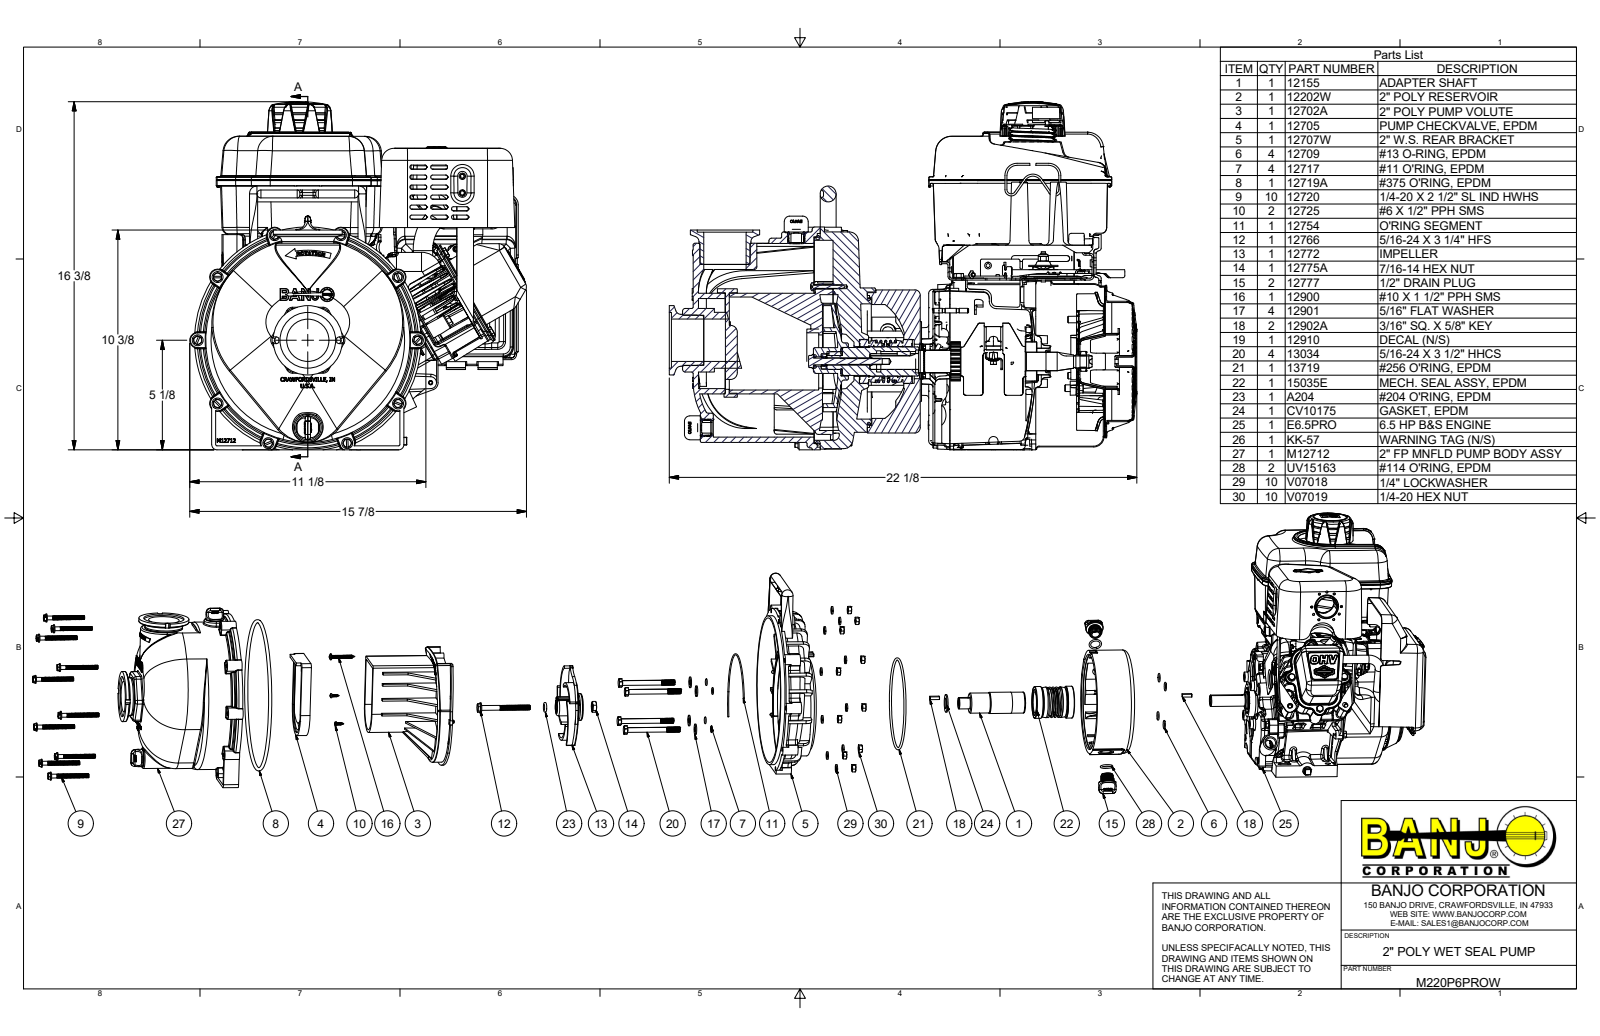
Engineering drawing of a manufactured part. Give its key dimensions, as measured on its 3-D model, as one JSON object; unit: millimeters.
{"part_name": "M220P6PROW; 12707W; 12707WX; 12703AWV (+8 more)", "step_written_by": "Autodesk Inventor 2017 (AUTOMOTIVE_DESIGN)", "units": "millimeters", "bodies": {"solids": 99, "faces": 21263, "planar": 5779, "cylindrical": 5805, "other": 9679}, "overall_size": [584.88, 417.62, 403.86], "volume_mm3": 3767000, "surface_area_mm2": 3383000, "round_holes": [[6.35, 13], [6.86, 11], [4.98, 10], [6.4, 10], [3.5, 9], [11.91, 8], [3.56, 7], [5.59, 7], [8.1, 6], [6.91, 5], [7.11, 5], [8.73, 5]], "round_bosses_or_shafts": [[7.02, 80], [6.35, 14], [12.7, 12], [13.21, 10], [12.42, 10], [4.83, 8], [7, 6], [4.88, 6]], "partial_cylinders_radius": [[1.52, 399], [0.76, 397], [3.05, 202], [2.29, 111], [3.17, 111], [6.35, 110], [0.38, 108], [2, 76]], "face_to_face_distances": [0.91, 2.03, 4.57, 1, 0.7, 2.18, 258.62, 120, 138.62, 1.19], "hole_center_spacings": [25, 132.08, 78.4, 12.94, 45.98, 48.3, 63.5, 43.31]}
